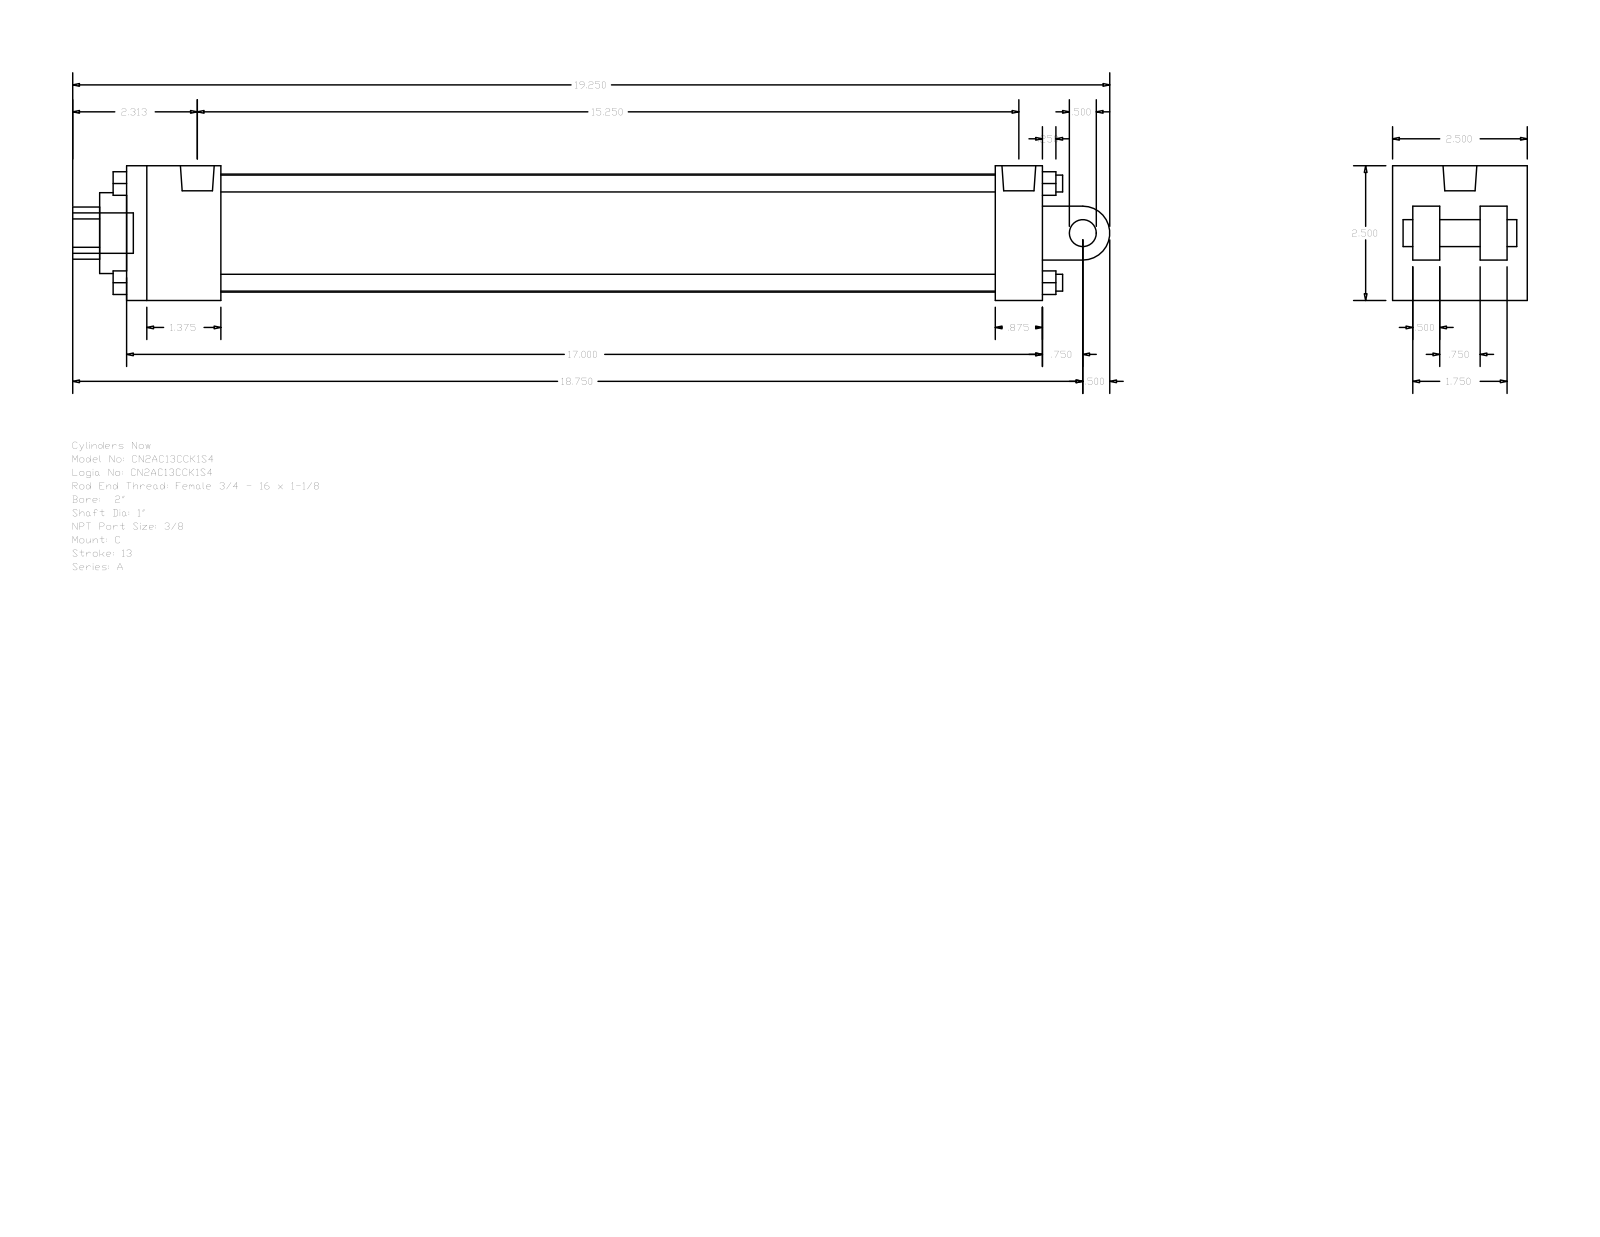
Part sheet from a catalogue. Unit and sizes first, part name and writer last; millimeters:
Units: millimetres
Overall size (bounding box): 488.95 × 63.5 × 63.5
Round holes (diameter × count): ⌀5.56 ×2, ⌀15.93 ×1, ⌀25.4 ×1, ⌀38.1 ×1, ⌀55.63 ×1
Round bosses / shafts (diameter × count): ⌀7.94 ×4, ⌀5.56 ×2, ⌀19.05 ×1, ⌀15.93 ×1, ⌀12.7 ×1
Partial cylindrical surfaces — rounded edges, fillets, slot ends (radius × count): R12.29 ×1, R12.7 ×1
Main face-to-face distances: 63.5, 22.22, 431.8, 44.45, 12.7, 9.52, 41.28, 387.35, 409.58, 365.13
Hole centre spacings: 3.98
Bodies: 0 solids, 135 faces (102 planar, 33 cylindrical, 0 other)
Part name (STEP PRODUCT): A_C__0200_1
STEP written by: GSSL Pune (CONFIG_CONTROL_DESIGN)
